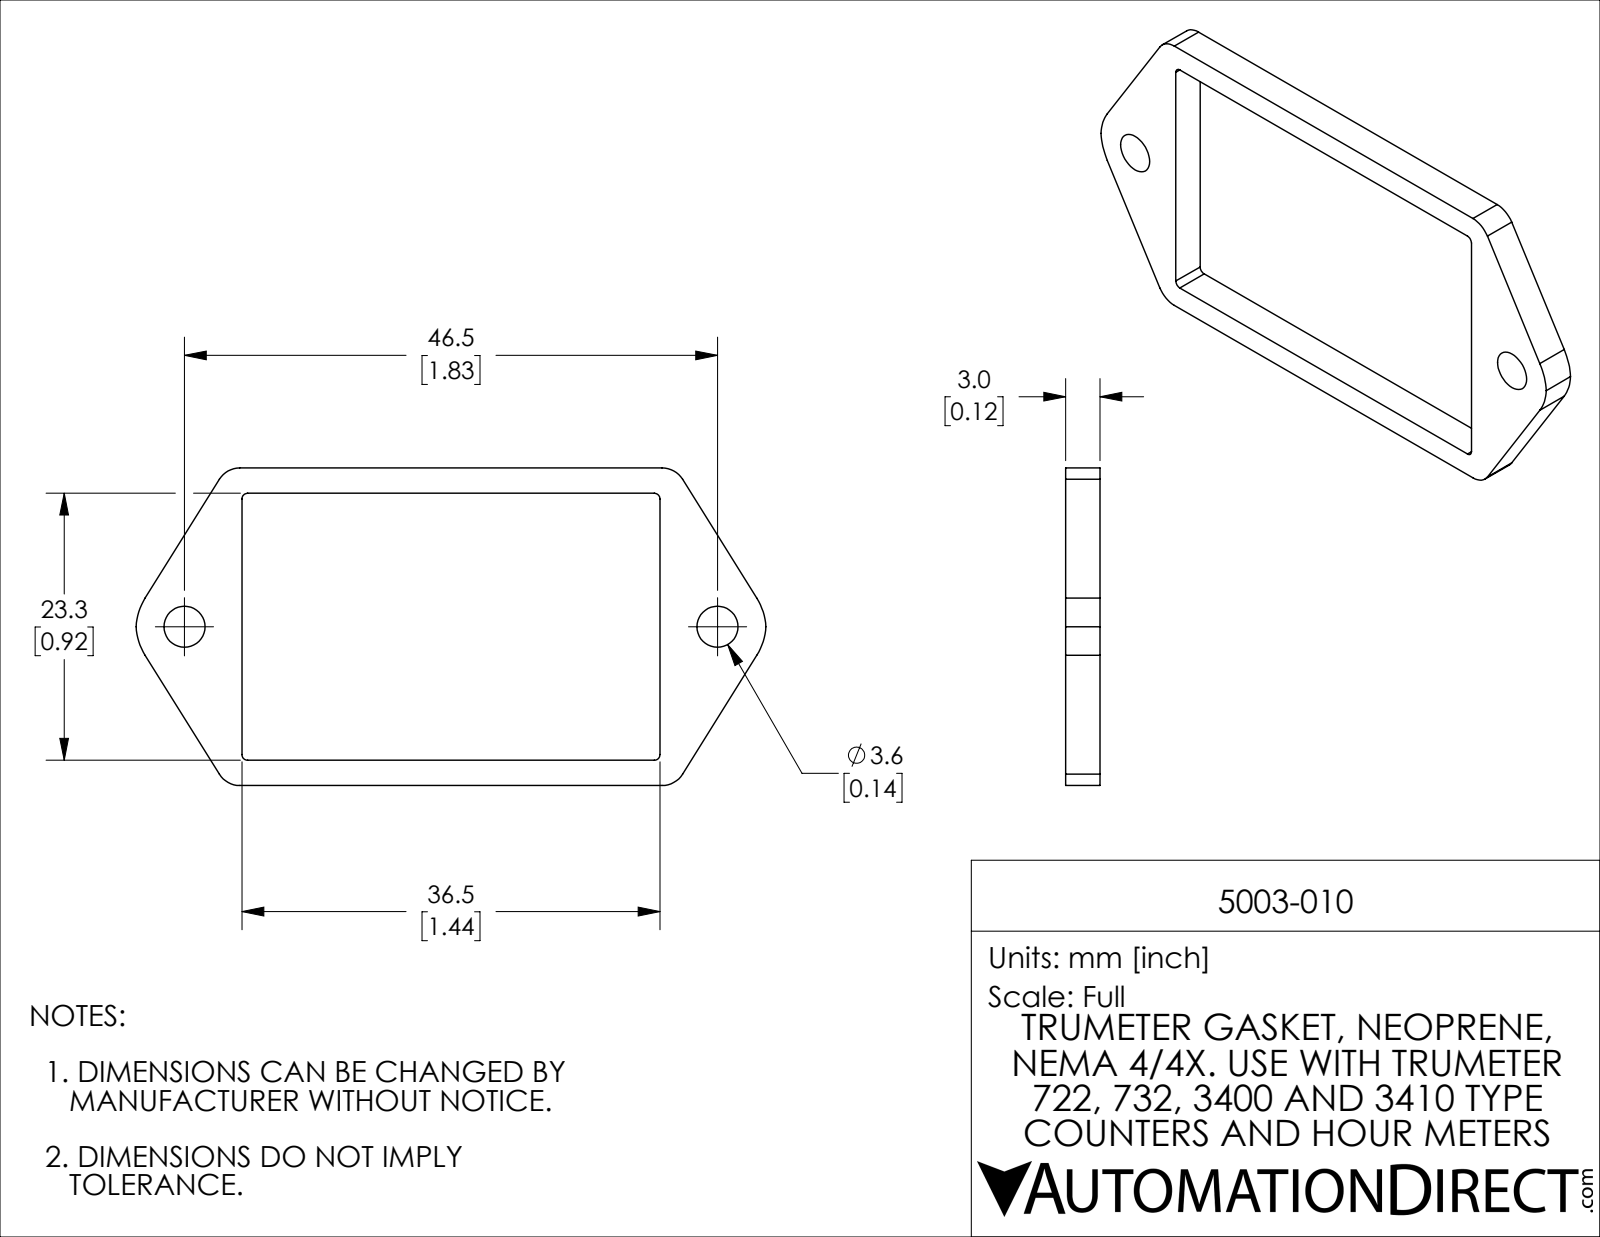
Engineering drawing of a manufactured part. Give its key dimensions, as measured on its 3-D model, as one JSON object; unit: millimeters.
{"part_name": "5003-010", "step_written_by": "SolidWorks 2021 (CONFIG_CONTROL_DESIGN)", "units": "millimeters", "bodies": {"solids": 1, "faces": 28, "planar": 12, "cylindrical": 16, "other": 0}, "overall_size": [55, 27.7, 3], "volume_mm3": 1400, "surface_area_mm2": 1754, "round_holes": [[3.6, 2]], "partial_cylinders_radius": [[0.5, 4], [2.1, 4], [5.3, 4]], "face_to_face_distances": [3, 2.2, 25.5, 27.7, 23.3, 47.9, 36.5], "hole_center_spacings": [46.5]}
